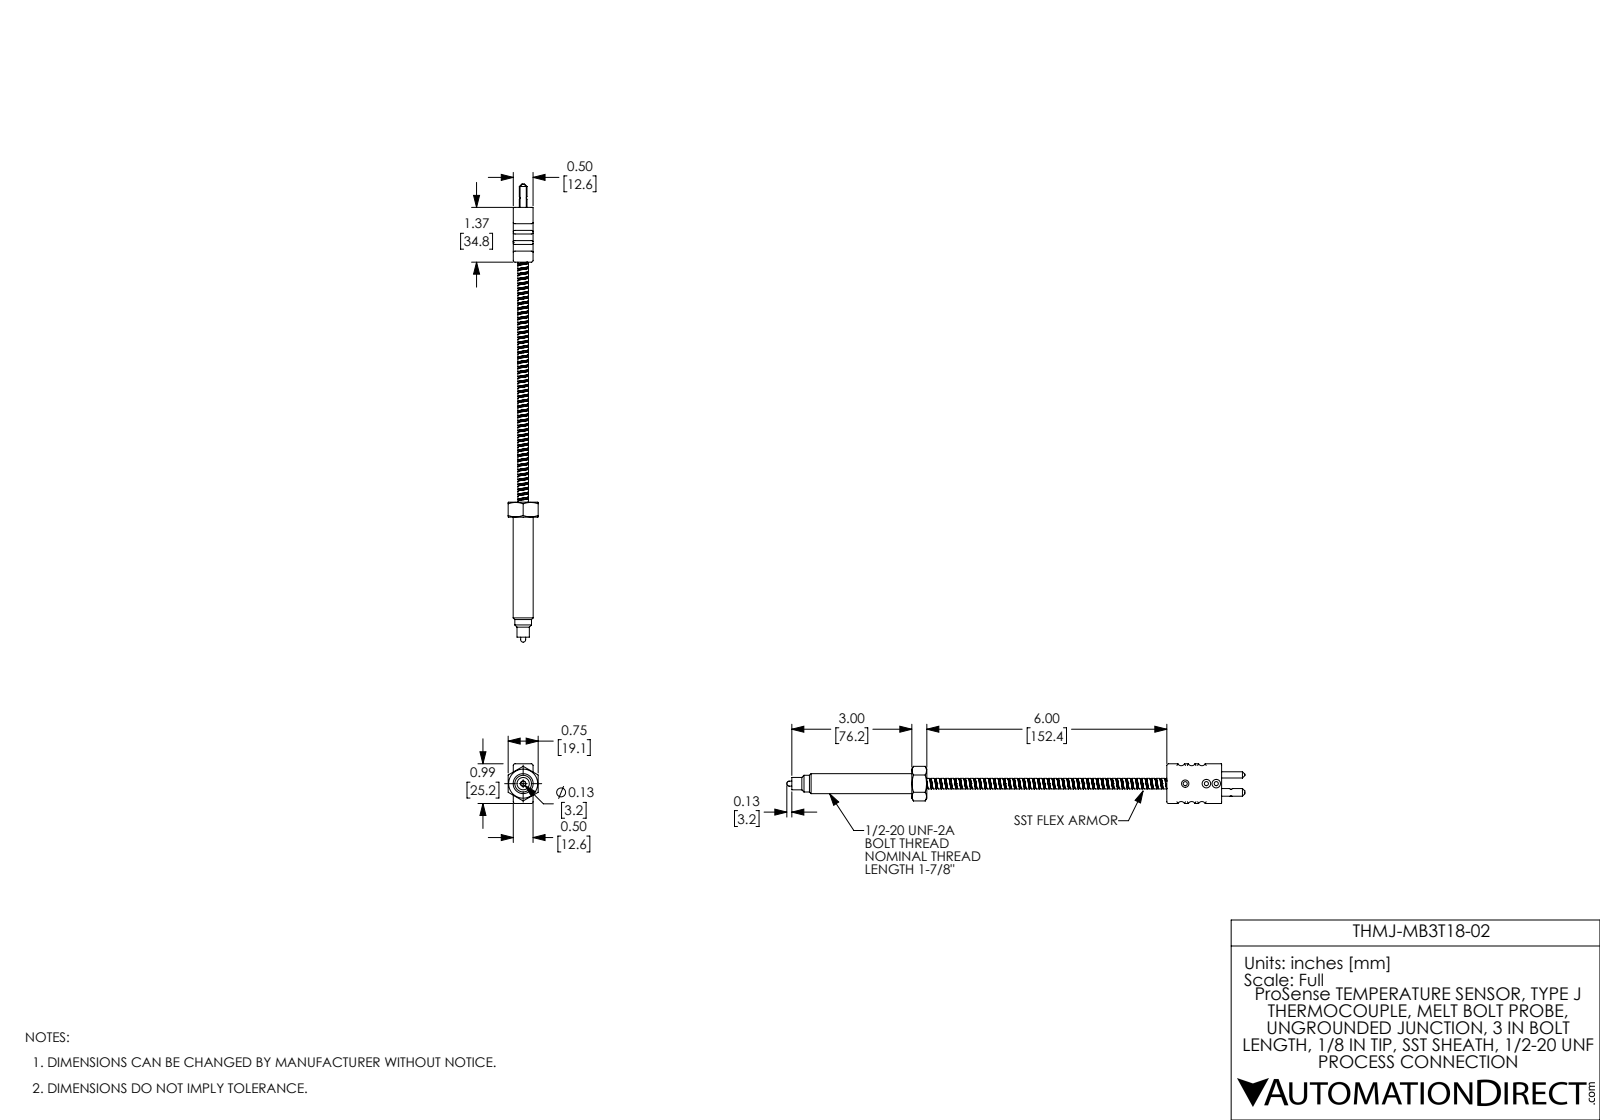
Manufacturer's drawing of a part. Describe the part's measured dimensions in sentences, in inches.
The part is named "THMJ-MB3T18-02". Its 3-D file was written by "SolidWorks 2017 (AUTOMOTIVE_DESIGN)". It is 3 solids with 312 faces: 69 planar, 172 cylindrical and 71 other. Overall it measures 11.451 by 0.993 by 0.75 inches. Its volume is 1.684 cubic inches and its surface area 19.16 square inches. Round holes: 2 of diameter 0.103, 2 of diameter 0.158, 1 of diameter 0.135, 1 of diameter 0.185, 1 of diameter 0.294, 1 of diameter 0.308. Round bosses or shafts: 1 of diameter 0.5, 1 of diameter 0.417, 1 of diameter 0.309, 1 of diameter 0.278, 1 of diameter 0.265, 1 of diameter 0.191, 1 of diameter 0.156, 1 of diameter 0.125. Partial cylindrical surfaces (rounded edges, fillets, slot ends): 8 of radius 0.045, 6 of radius 0.095, 4 of radius 0.01. The main face-to-face distances are 0.495, 0.75, 7.369, 0.993, 0.127, 0.622, 1.369, 6, 7.744, 6.375. The hole center spacings are 0.217, 0.328, 0.572, 0.247, 0.433, 0.529, 0.776.
